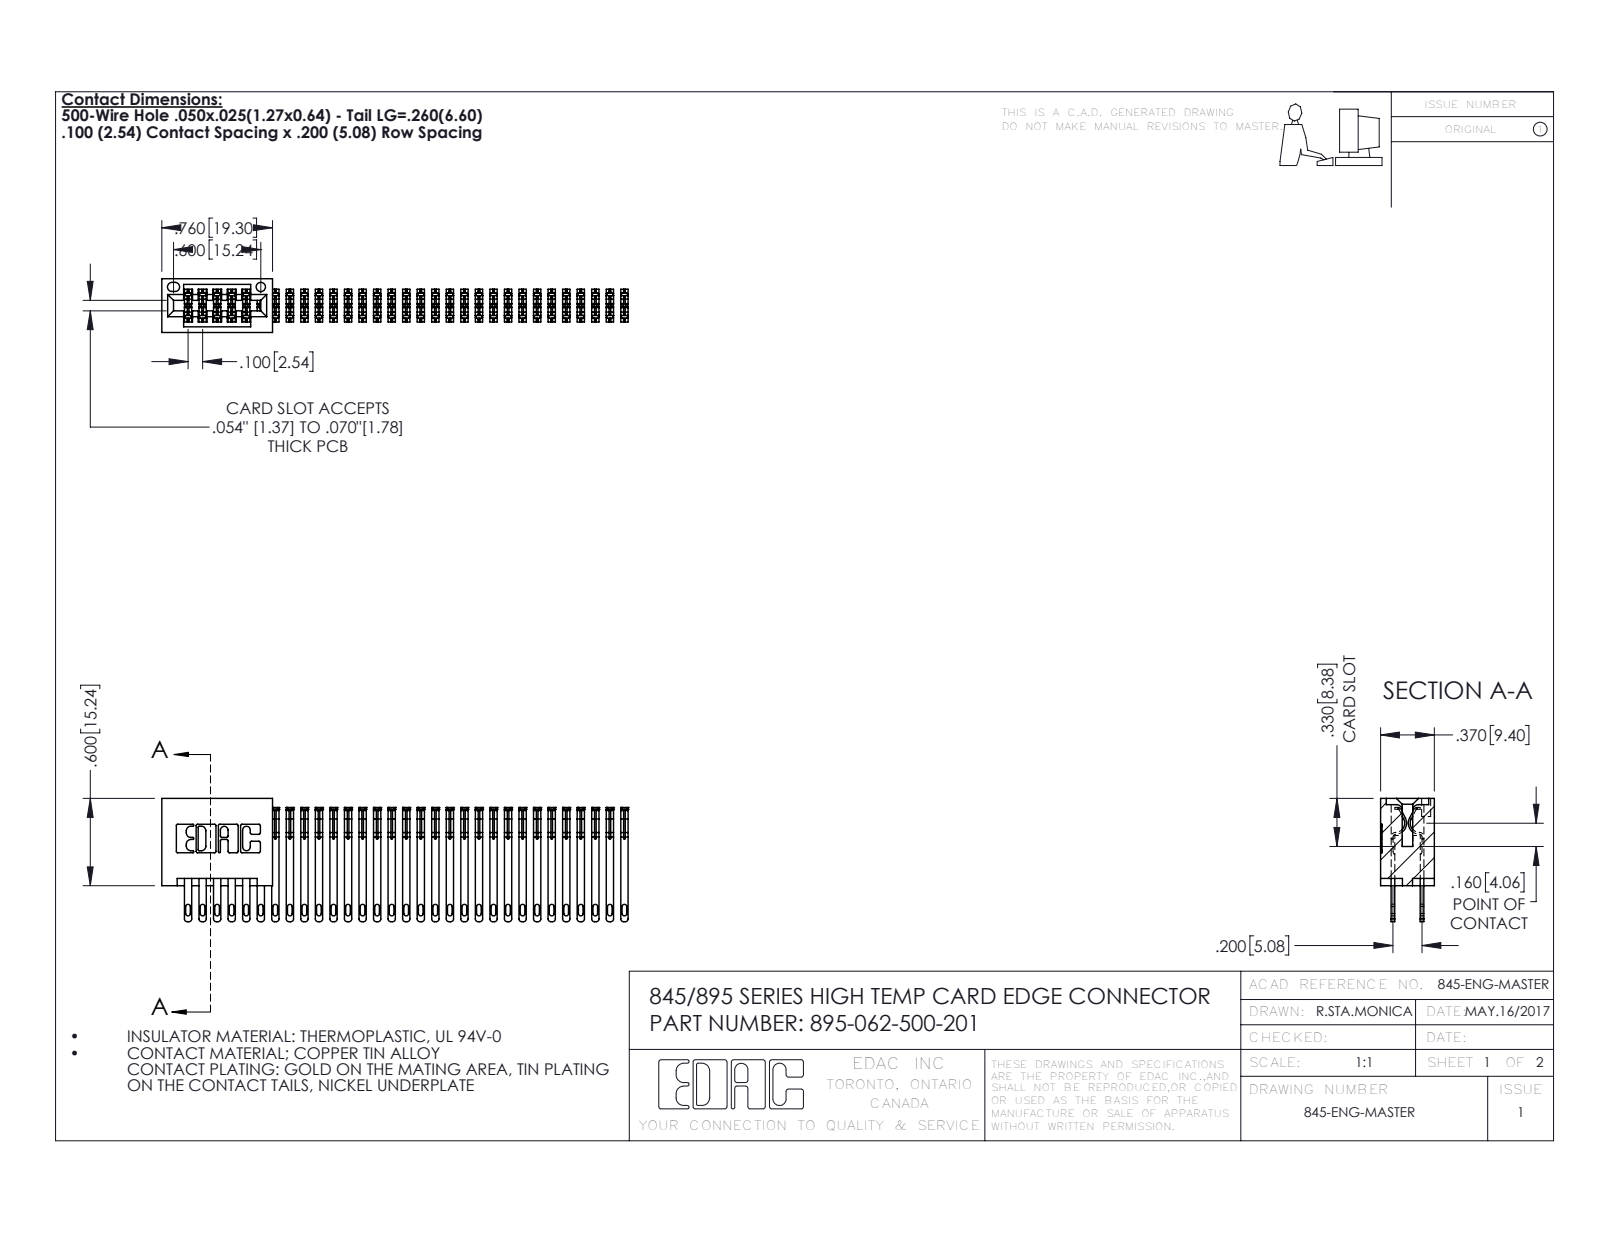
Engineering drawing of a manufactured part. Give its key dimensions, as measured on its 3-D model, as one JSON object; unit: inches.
{"part_name": "845 Part_No Mounting Lugs; 345-292-001_345-293-100; 895-062-500-201", "step_written_by": "SolidWorks 2020 (CONFIG_CONTROL_DESIGN)", "units": "inches", "bodies": {"solids": 63, "faces": 2970, "planar": 1750, "cylindrical": 1220, "other": 0}, "overall_size": [3.36, 0.847, 0.37], "volume_in3": 0.549, "surface_area_in2": 21.73, "round_holes": [[0.064, 1]], "partial_cylinders_radius": [[0.006, 93], [0.016, 62], [0.02, 62], [0.01, 22], [0.007, 6], [0.031, 6], [0.026, 3], [0.014, 2]], "face_to_face_distances": [0.298, 0.072, 0.2, 0.098, 0.272, 0.025, 0.37, 0.225, 0.175, 0.149]}
